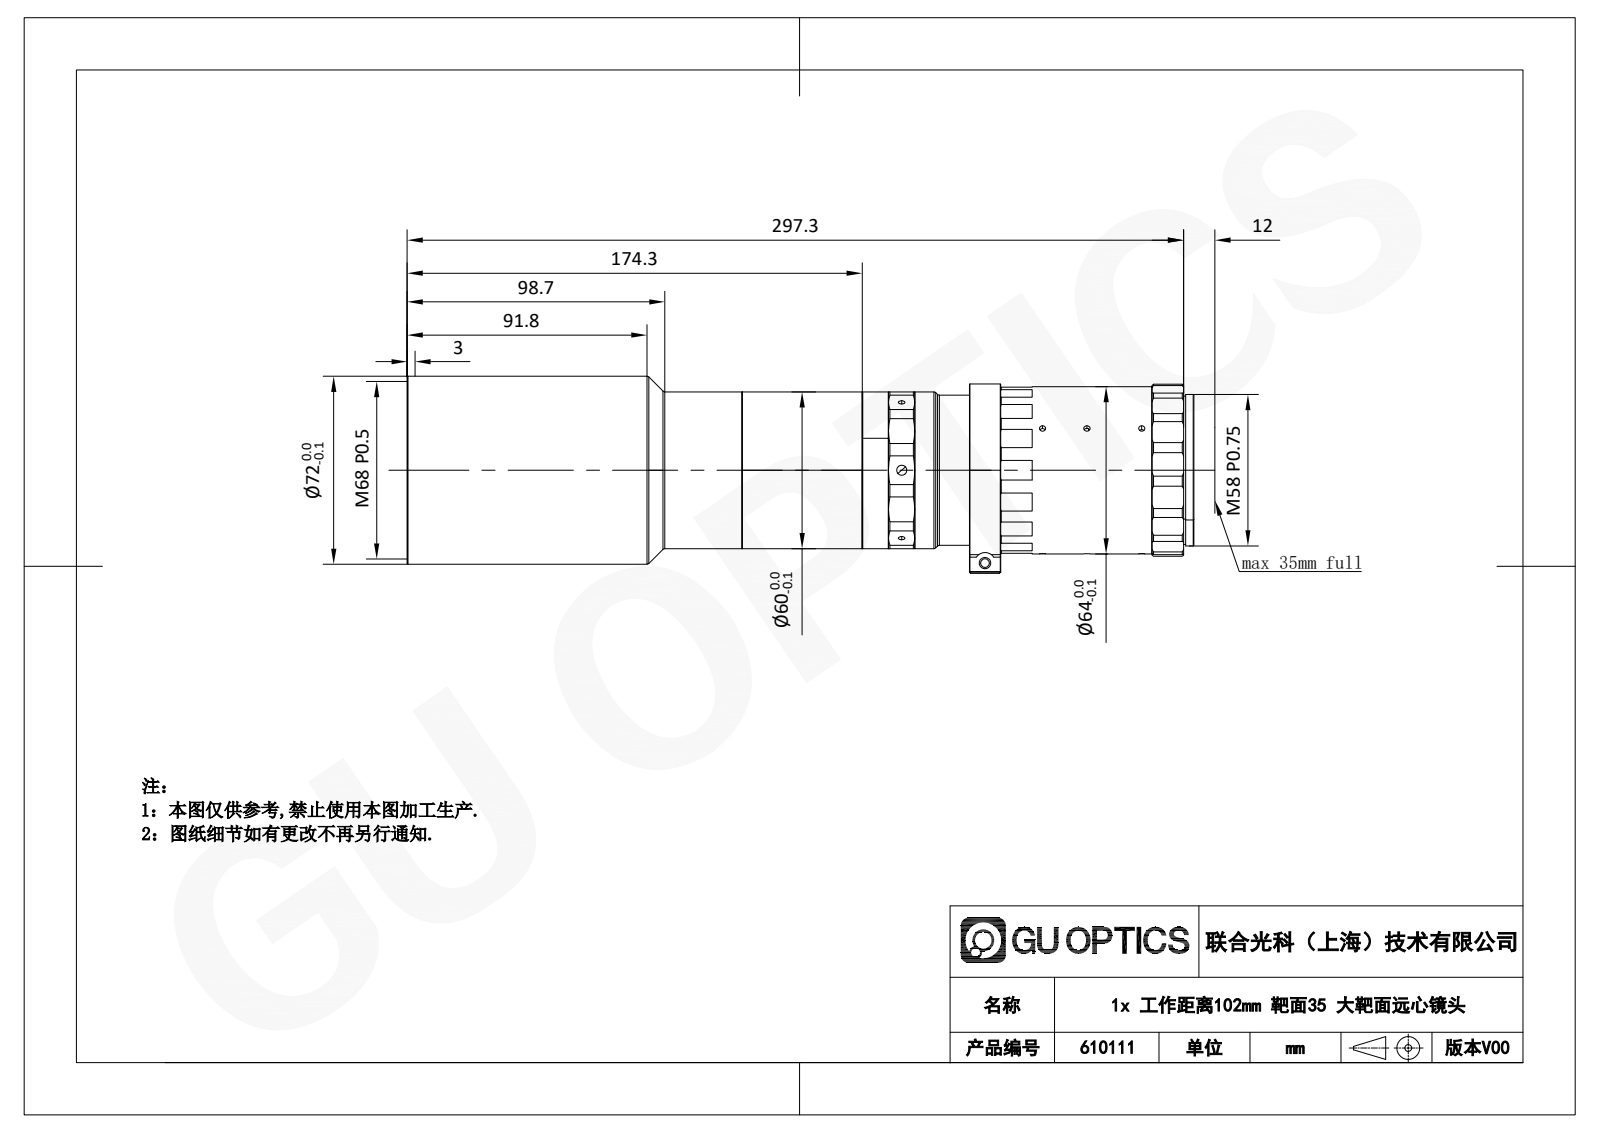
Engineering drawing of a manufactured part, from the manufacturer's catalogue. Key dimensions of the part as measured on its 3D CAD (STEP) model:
Part name (STEP PRODUCT): DTCA35F-44-G-M58-AL
STEP written by: SolidWorks 2017 (CONFIG_CONTROL_DESIGN)
Units: millimetres
Bodies: 1 solid, 445 faces (83 planar, 173 cylindrical, 189 other)
Overall size (bounding box): 301.3 × 75.49 × 72
Volume: 940 108 mm³ · Surface area: 80 834 mm²
Round holes (diameter × count): ⌀2.4 ×9, ⌀2.5 ×3, ⌀2.2 ×1, ⌀3.4 ×1, ⌀4.5 ×1, ⌀52.5 ×1, ⌀55.5 ×1, ⌀58 ×1, ⌀62.3 ×1, ⌀67.5 ×1
Round bosses / shafts (diameter × count): ⌀72 ×1, ⌀66 ×1, ⌀64 ×1, ⌀62 ×1, ⌀61 ×1, ⌀60 ×1, ⌀57.5 ×1, ⌀57.21 ×1
Partial cylindrical surfaces — rounded edges, fillets, slot ends (radius × count): R15 ×32, R1 ×2, R1.55 ×1, R4 ×1, R39.5 ×1
Main face-to-face distances: 82, 60, 12, 70, 24, 62, 20, 50, 215.3, 227.3
Hole centre spacings: 17, 21, 38, 47.75
